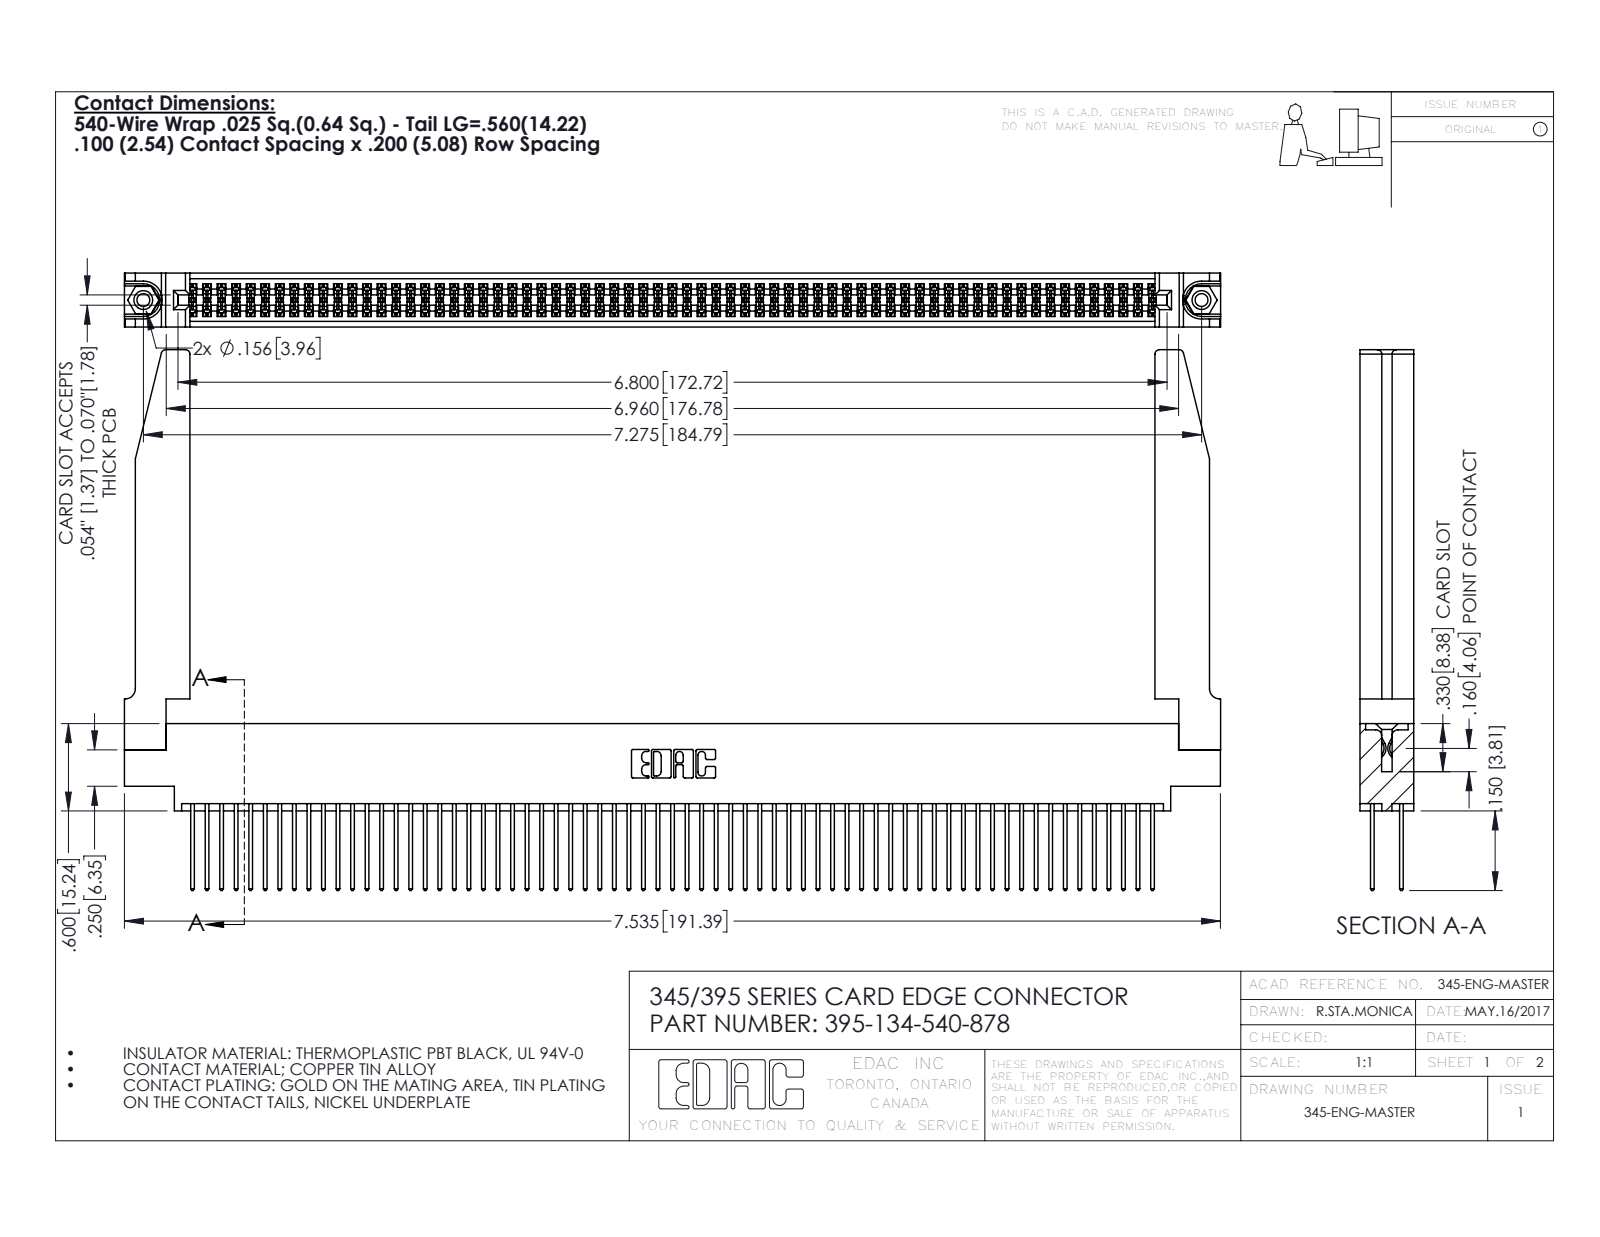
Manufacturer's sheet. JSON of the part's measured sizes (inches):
{"part_name": "345-220-078_345-220-078; 345-250-001_345-250-001-102; 345 Part_0.170 Offset - 0.156 Dia-TH; 395-134-540-878 (+1 more)", "step_written_by": "SolidWorks 2016 (CONFIG_CONTROL_DESIGN)", "units": "inches", "bodies": {"solids": 139, "faces": 7064, "planar": 4648, "cylindrical": 2364, "other": 52}, "overall_size": [7.536, 3.717, 0.37], "volume_in3": 1.647, "surface_area_in2": 59.26, "round_holes": [[0.089, 2], [0.125, 2], [0.156, 2], [0.064, 1]], "round_bosses_or_shafts": [[0.155, 2]], "partial_cylinders_radius": [[0.006, 201], [0.01, 134], [0.01, 22], [0.03, 8], [0.007, 6], [0.031, 6], [0.026, 3], [0.014, 2]], "face_to_face_distances": [0.072, 0.298, 0.37, 0.098, 0.272, 0.025, 0.2, 0.225, 0.175, 0.149], "hole_center_spacings": [0.27, 7.039, 7.275]}
